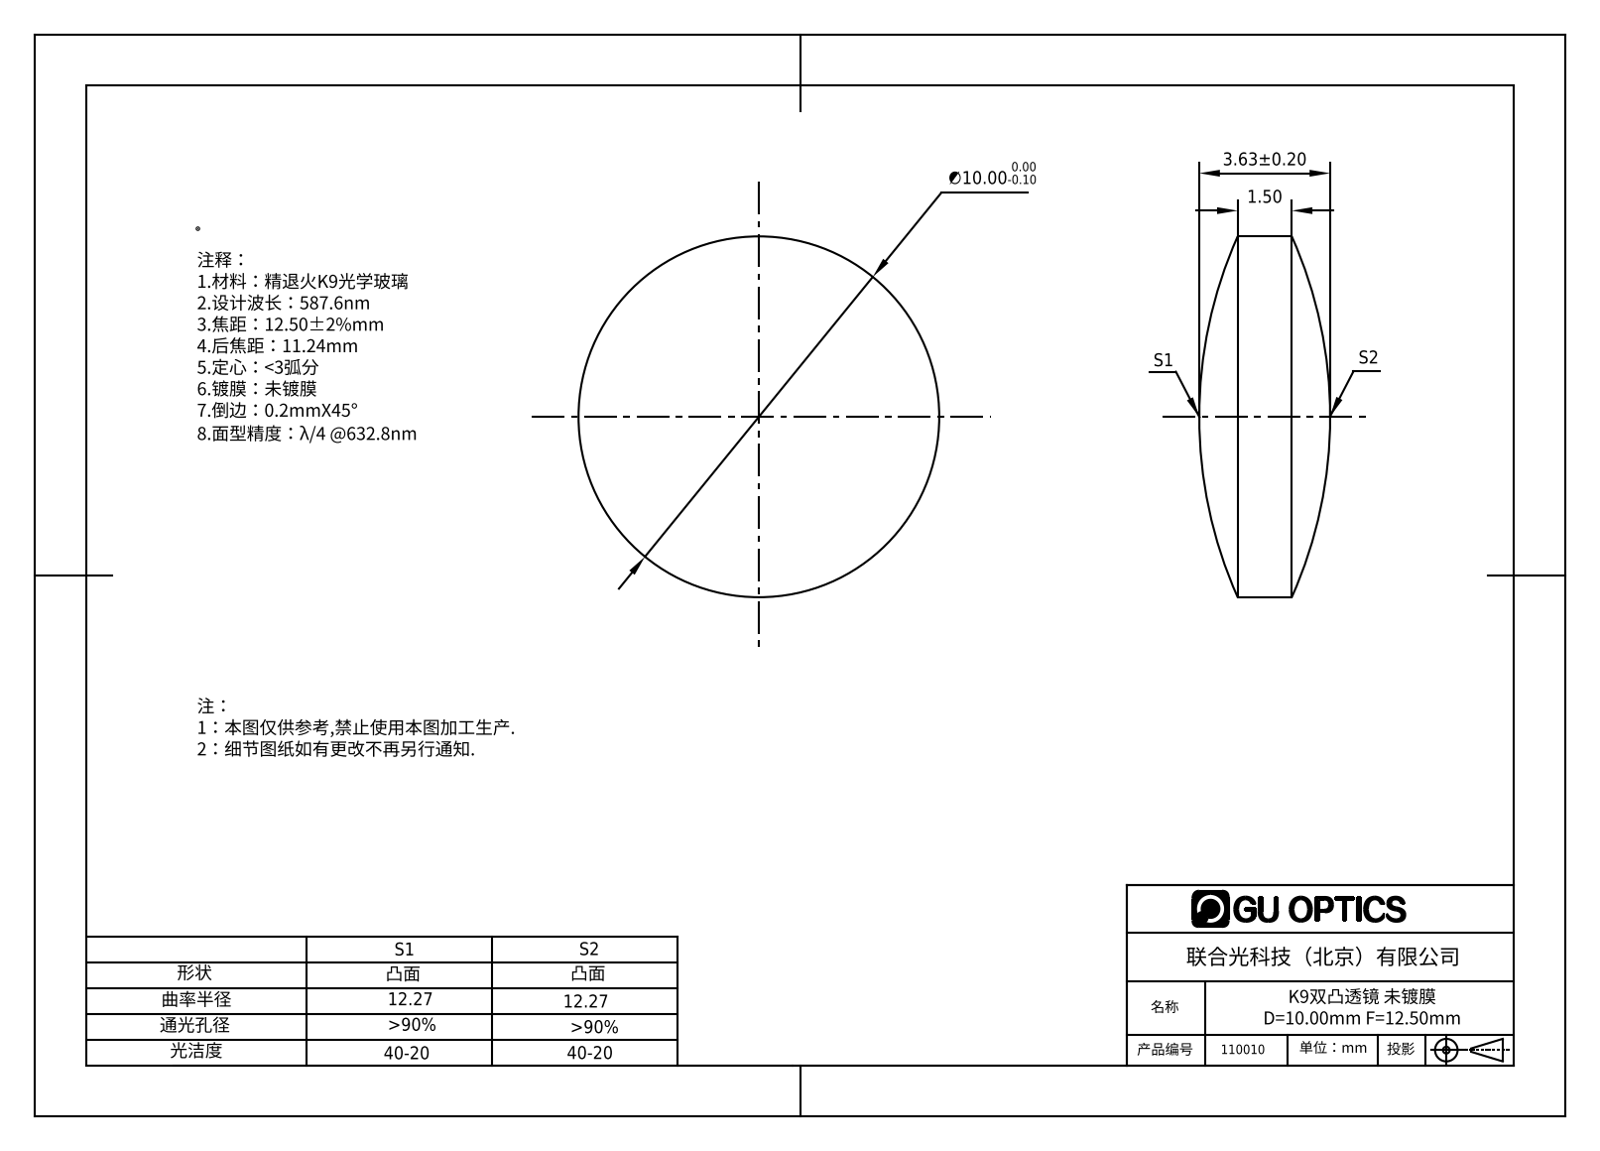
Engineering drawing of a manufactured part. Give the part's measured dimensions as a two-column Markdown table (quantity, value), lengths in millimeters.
| quantity | value |
| --- | --- |
| part name | 110010 |
| STEP written by | SolidWorks 2016 (CONFIG_CONTROL_DESIGN) |
| units | millimeters |
| bodies | 1 solid, 6 faces (0 planar, 2 cylindrical, 4 other) |
| overall size | 70 × 70 × 25.4 |
| volume | 69 517 mm³ |
| surface area | 10 355 mm² |
| round bosses / shafts (diameter × count) | 70 × 1 |
